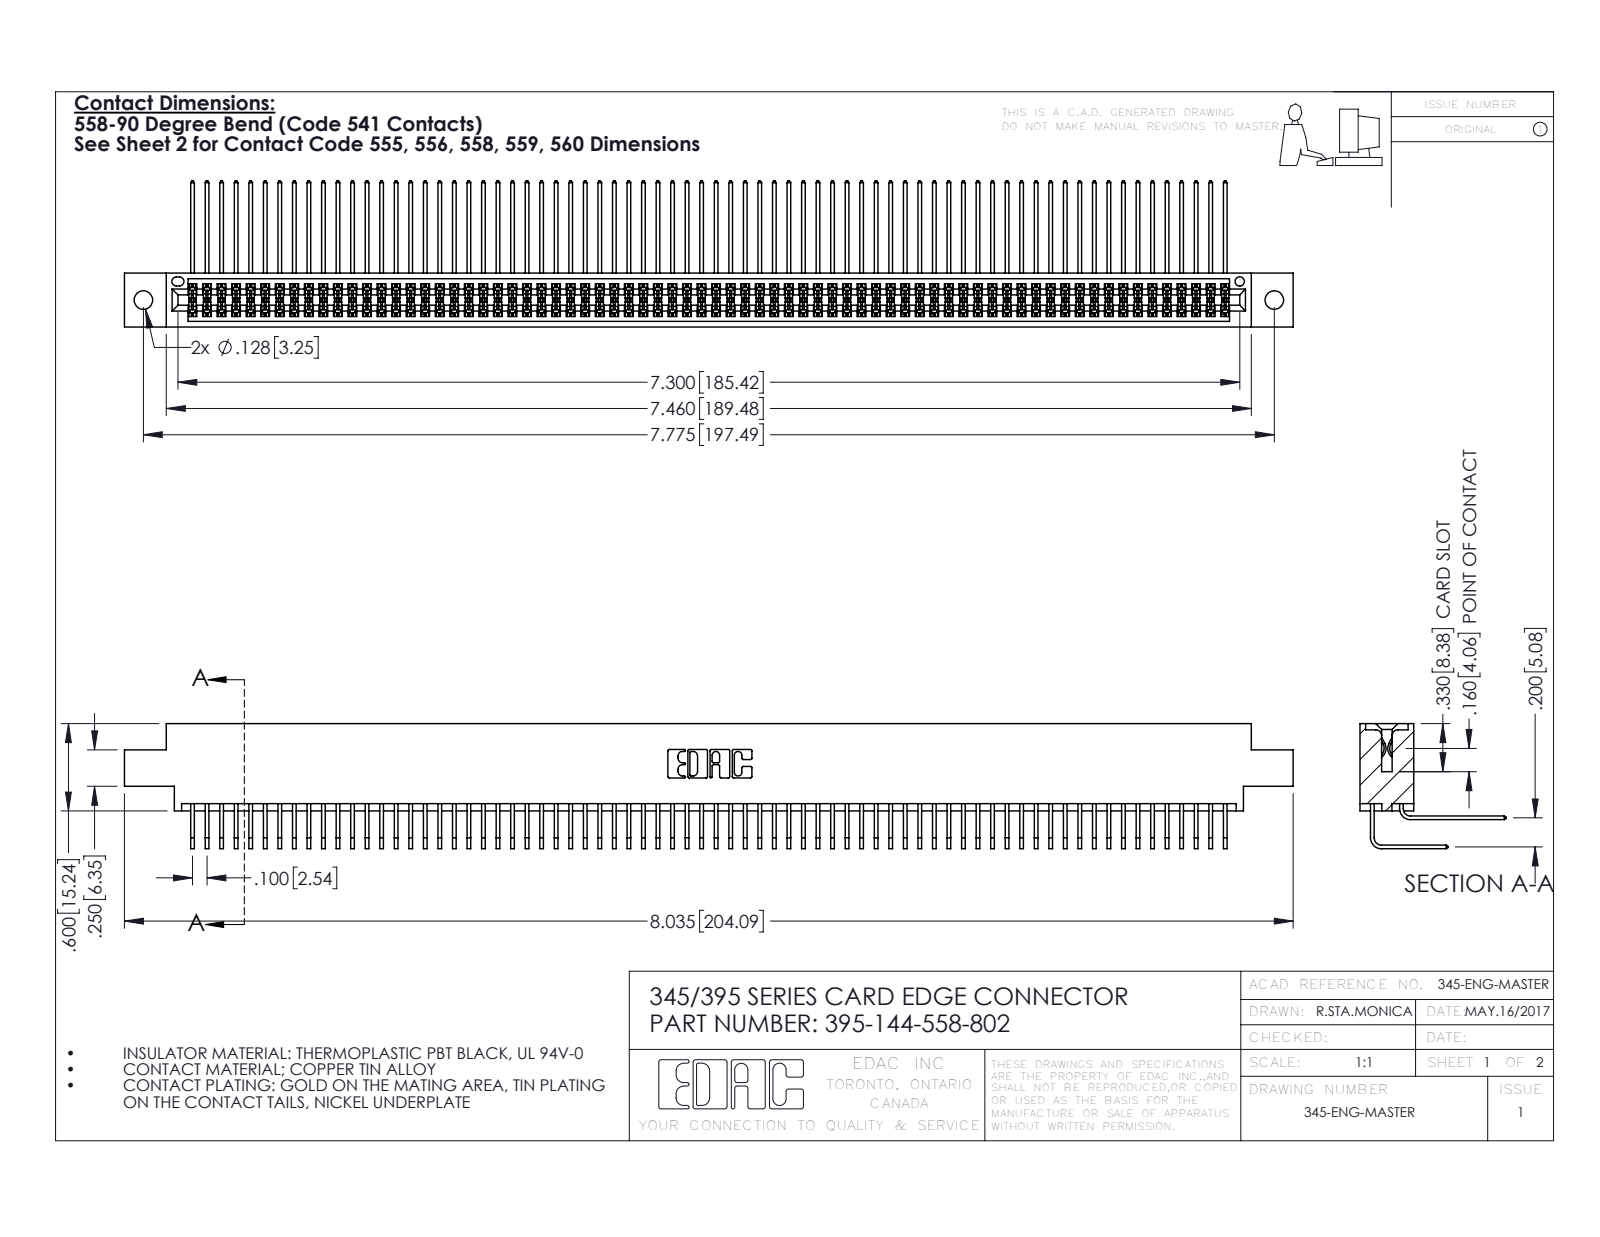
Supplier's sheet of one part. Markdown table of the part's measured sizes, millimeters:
| quantity | value |
| --- | --- |
| part name | 345-292-001_558 559 Tail - 1; 345 Part_0.170 Offset - 0.128 Dia; 345-292-001_558 Tail - 2; 395-144-558-802 |
| STEP written by | SolidWorks 2016 (CONFIG_CONTROL_DESIGN) |
| units | millimeters |
| bodies | 145 solids, 7618 faces (5124 planar, 2494 cylindrical, 0 other) |
| overall size | 204.1 × 25.5 × 21.8 |
| volume | 20 780 mm³ |
| surface area | 35 080 mm² |
| round holes (diameter × count) | 3.3 × 2, 1.6 × 1 |
| partial cylindrical surfaces (radius × count) | 0.2 × 216, 0.3 × 22, 0.2 × 6, 0.8 × 6, 0.7 × 3, 0.4 × 2, 0.5 × 2, 0.6 × 2 |
| main face-to-face distances | 1.8, 7.6, 5.1, 9.4, 2.5, 6.9, 0.6, 5.7, 4.4, 0.6 |
| hole center spacings | 6.9, 191.5, 197.5 |
